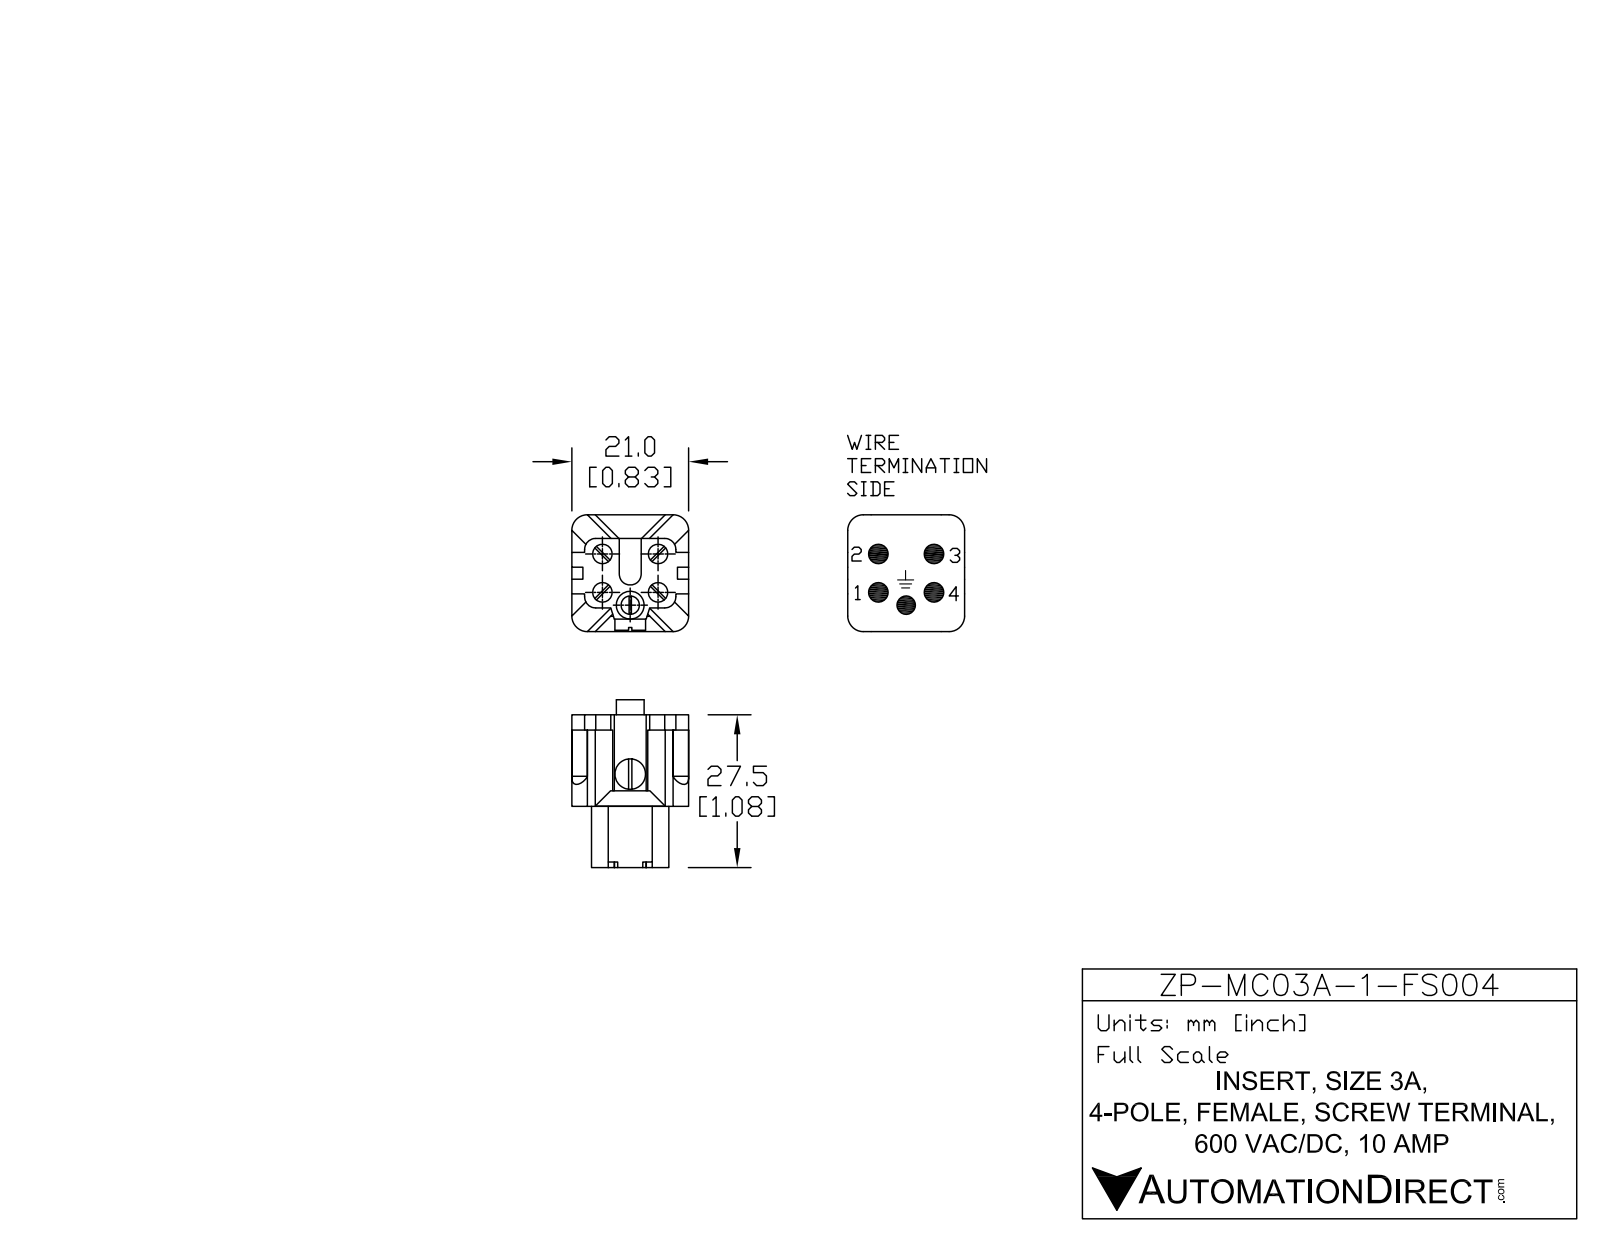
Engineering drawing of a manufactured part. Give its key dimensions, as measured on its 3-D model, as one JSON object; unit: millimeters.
{"part_name": "ZP-3A-4-FS-INSERT", "step_written_by": "SolidWorks 2011 (AUTOMOTIVE_DESIGN)", "units": "millimeters", "bodies": {"solids": 1, "faces": 154, "planar": 107, "cylindrical": 47, "other": 0}, "overall_size": [30.15, 21, 21], "volume_mm3": 5885, "surface_area_mm2": 4516, "round_holes": [[1.8, 4], [3.5, 4], [3.1, 1], [3.3, 1]], "round_bosses_or_shafts": [[5.5, 1], [5, 1]], "partial_cylinders_radius": [[1.5, 6], [2, 6], [3, 6], [2.8, 4], [1, 2], [1.98, 2], [2.06, 2], [2.59, 2]], "face_to_face_distances": [17.45, 1, 21, 4.94, 3.55, 16.45, 3.94, 12.7, 10, 13.9], "hole_center_spacings": [9.51, 0.62, 0.63, 4.59, 5.02, 5.24, 5.5, 6.15]}
